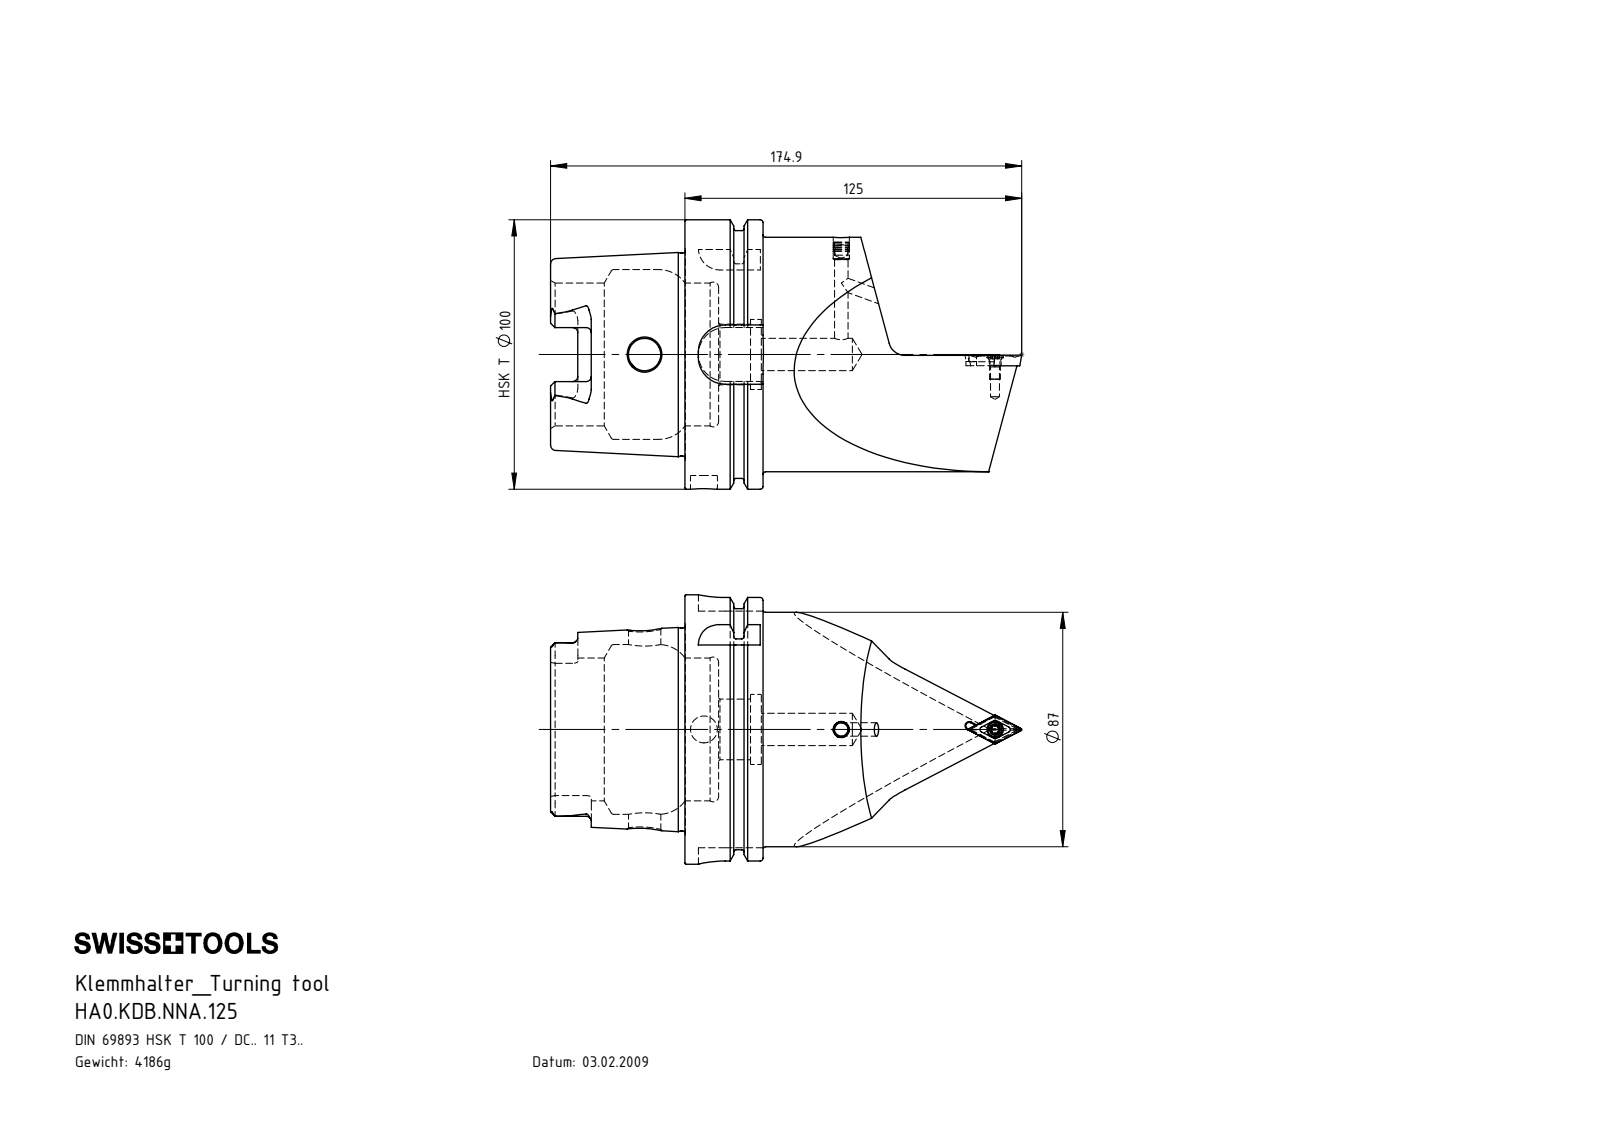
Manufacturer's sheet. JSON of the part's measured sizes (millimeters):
{"part_name": "WCB-ER2.001.009_A; HA0.KDB.NNA.125; DCMT11T304; KVT_MB_600_060 (+1 more)", "step_written_by": "SolidWorks 2009 (CONFIG_CONTROL_DESIGN)", "units": "millimeters", "bodies": {"solids": 5, "faces": 297, "planar": 76, "cylindrical": 85, "other": 136}, "overall_size": [174.91, 100, 100], "volume_mm3": 532968, "surface_area_mm2": 67142, "round_holes": [[5, 2], [12, 2], [3.3, 1], [4.4, 1], [6.1, 1], [10, 1], [22.5, 1], [26, 1], [53, 1], [63, 1]], "round_bosses_or_shafts": [[100, 1], [91.95, 1], [87, 1], [75.26, 1], [6, 1], [5.25, 1], [4, 1]], "partial_cylinders_radius": [[0.34, 6], [0.59, 6], [1.9, 6], [10, 3], [4.83, 2], [4.88, 2], [1.25, 1], [6, 1]], "face_to_face_distances": [12.45, 28.95, 16.5, 49.9, 62.35, 78.85, 87.8, 78.2, 28.3, 15.85], "hole_center_spacings": [51, 57.05, 57.15, 108.05, 108.15]}
